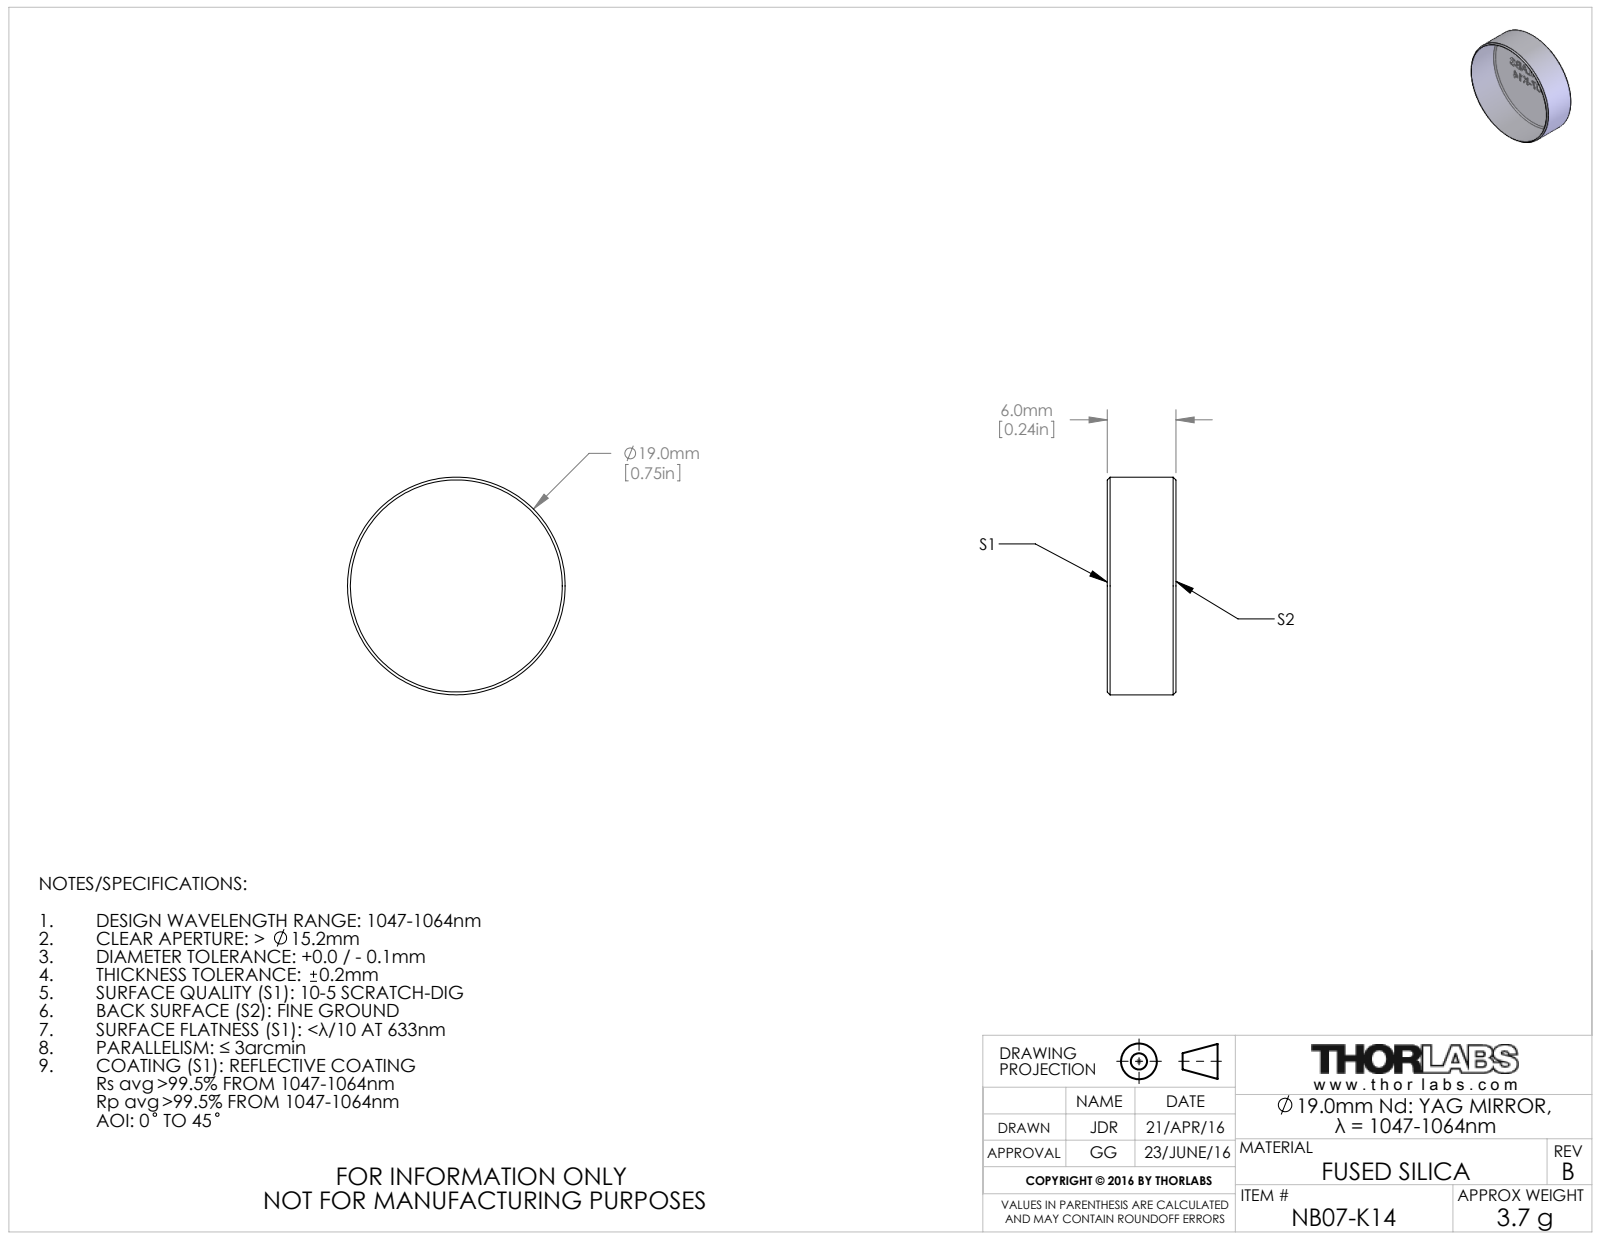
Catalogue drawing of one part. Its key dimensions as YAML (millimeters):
part_name: "TTN024113-E0W"
step_written_by: "SolidWorks 2016 (CONFIG_CONTROL_DESIGN)"
units: millimeters
bodies: {solids: 1, faces: 218, planar: 145, cylindrical: 2, other: 71}
overall_size: [19, 19, 6]
volume: 1700
surface_area: 908
round_bosses_or_shafts:
  - {diameter: 19, count: 1}
face_to_face_distances: [6, 1.5, 1, 2.4, 1.9, 0.9, 4.1, 2.1, 0.7, 0.5]
